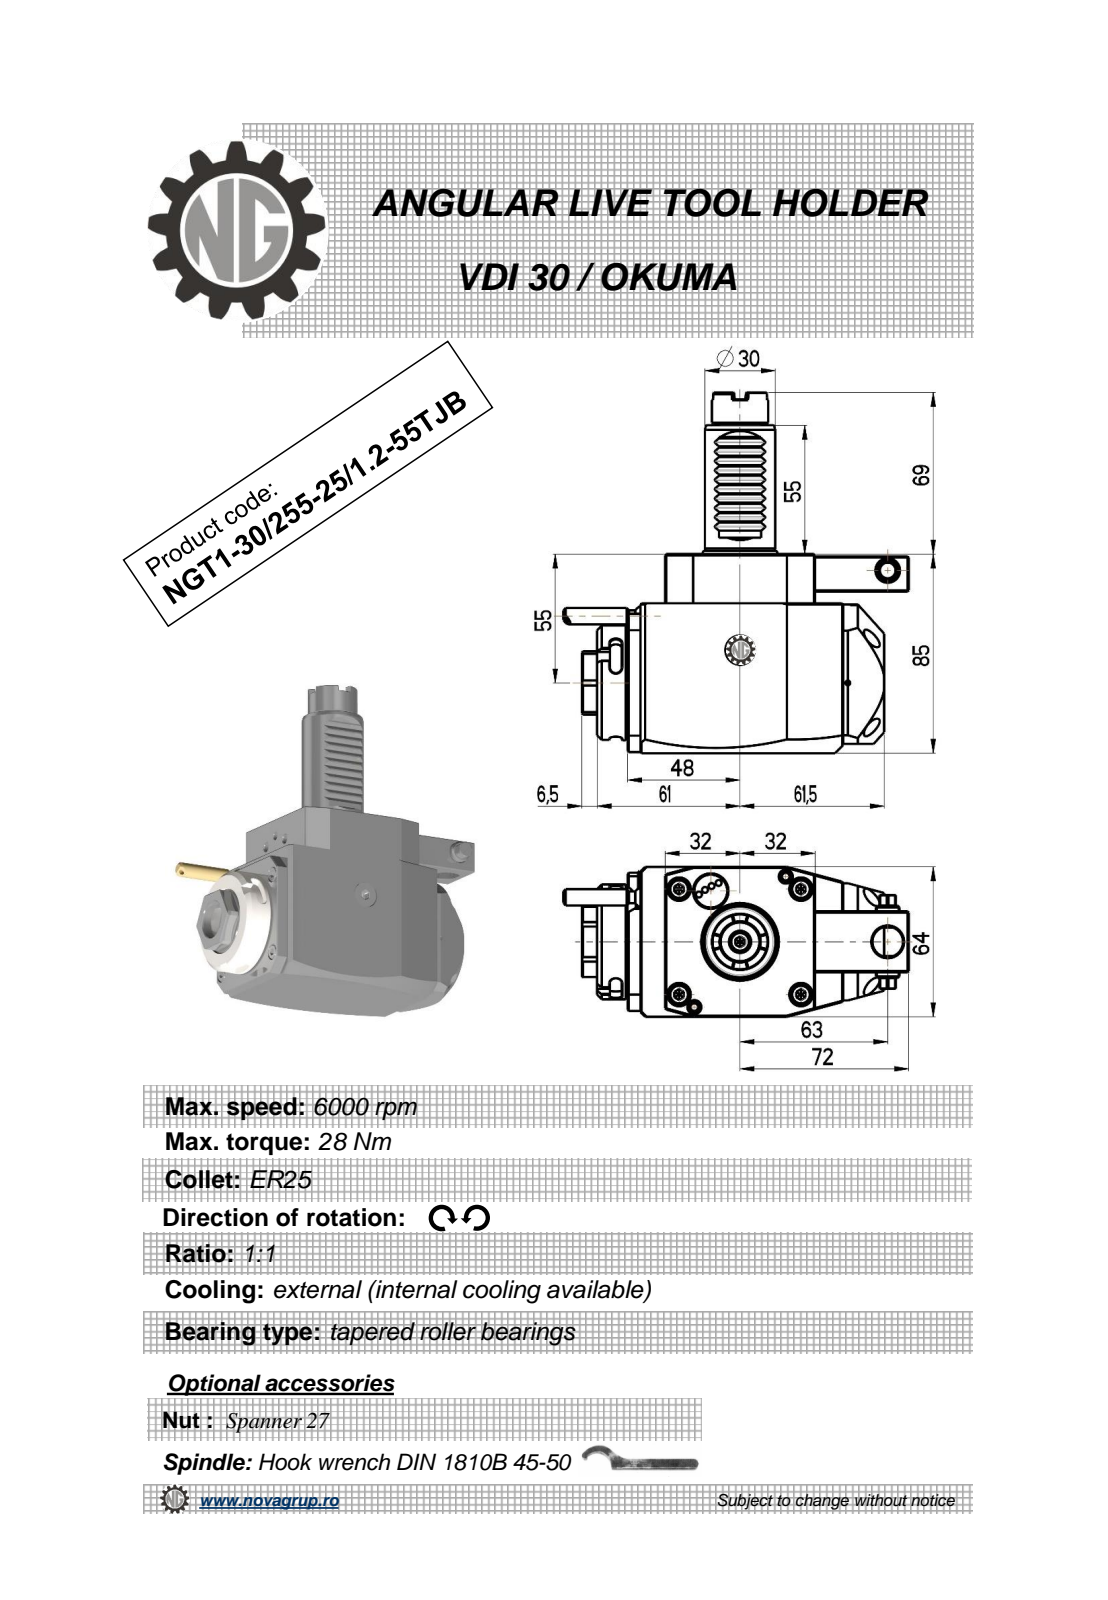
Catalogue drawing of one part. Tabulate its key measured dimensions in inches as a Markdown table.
| quantity | value |
| --- | --- |
| part name | NGT1_30_255_25_1_2_55TJB |
| STEP written by | PRO/ENGINEER BY PARAMETRIC TECHNOLOGY CORPORATION, 2010280 (CONFIG_CONTROL_DESIGN) |
| units | inches |
| bodies | 1 solid, 391 faces (207 planar, 82 cylindrical, 102 other) |
| overall size | 6.063 × 5.802 × 2.52 |
| volume | 34.55 in³ |
| surface area | 82.91 in² |
| round holes (diameter × count) | 0.098 × 1, 0.118 × 1, 0.374 × 1, 0.512 × 1, 0.669 × 1, 0.709 × 1 |
| round bosses / shafts (diameter × count) | 0.315 × 2, 1.929 × 1, 1.654 × 1, 1.181 × 1, 0.945 × 1, 0.821 × 1, 0.394 × 1, 0.276 × 1 |
| partial cylindrical surfaces (radius × count) | 0.012 × 10, 0.098 × 6, 7.087 × 2, 0.152 × 1, 0.167 × 1, 0.177 × 1, 0.591 × 1, 0.846 × 1 |
| main face-to-face distances | 2.52, 3.346, 0.63, 0.748, 4.311, 0.512, 0.827, 4.823, 3.15, 1.142 |
| hole center spacings | 1.03, 1.348, 1.831, 2.48 |
